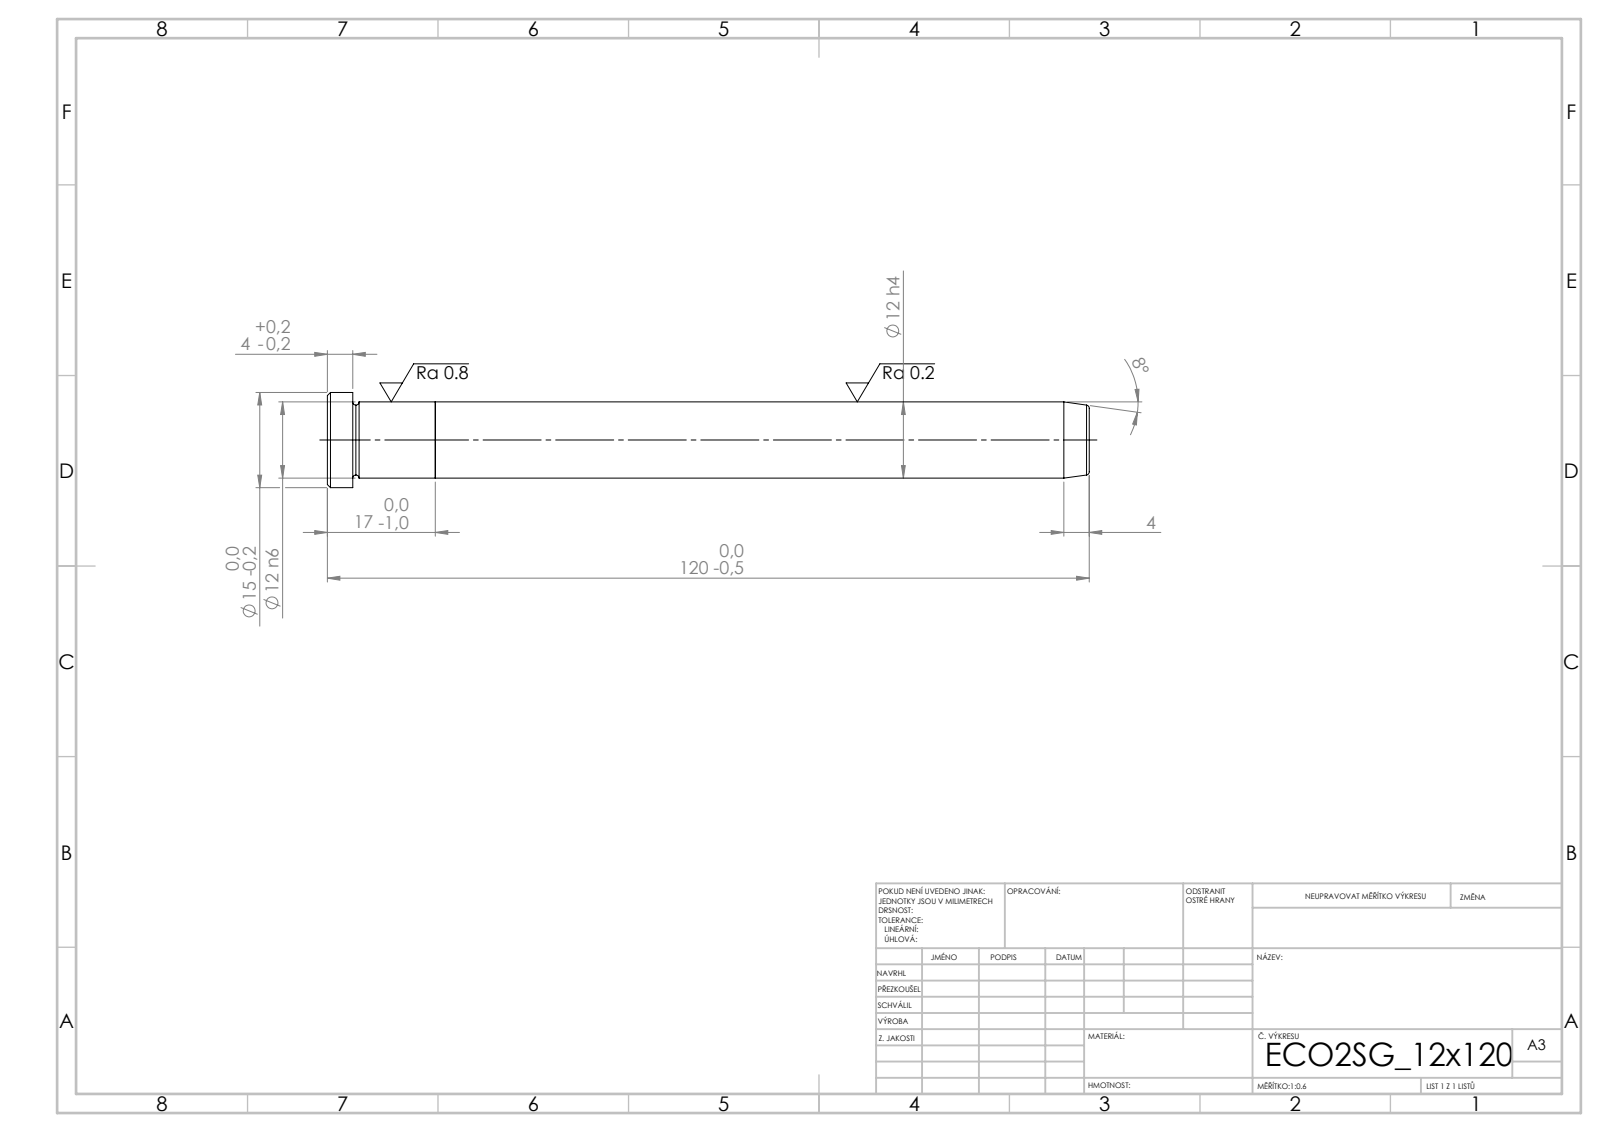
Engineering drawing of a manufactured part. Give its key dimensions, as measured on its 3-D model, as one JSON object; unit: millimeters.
{"step_written_by": "SolidWorks 2019 (CONFIG_CONTROL_DESIGN)", "units": "millimeters", "bodies": {"solids": 2, "faces": 21, "planar": 5, "cylindrical": 6, "other": 10}, "overall_size": [120, 15, 15], "volume_mm3": 13764, "surface_area_mm2": 5114, "round_bosses_or_shafts": [[15, 1], [12, 1]], "face_to_face_distances": [17, 103, 120, 116, 13, 4]}
